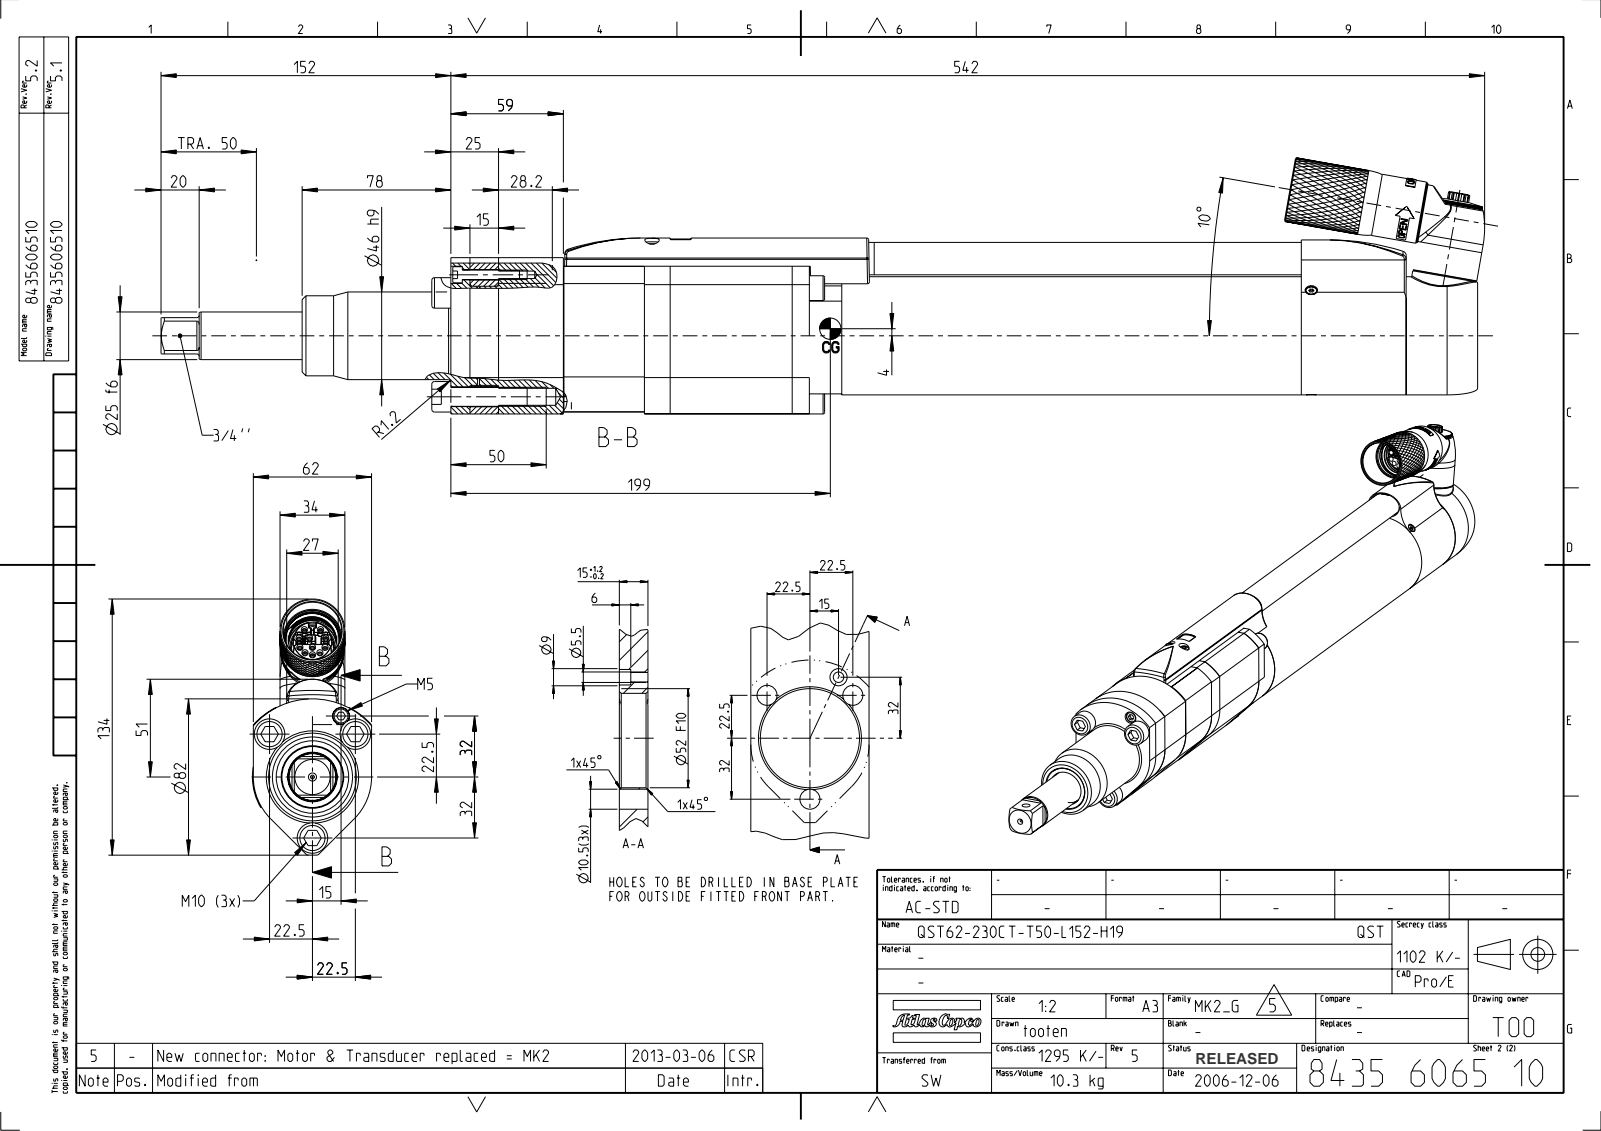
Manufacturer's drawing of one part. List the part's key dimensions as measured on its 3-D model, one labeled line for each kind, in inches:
Part name (STEP PRODUCT): QST62_REARCOVER_02; QST_CONNECTOR_02; QST62_230_CT_BODY; QST62_SPACER_01 (+3 more)
STEP written by: PRO/ENGINEER BY PARAMETRIC TECHNOLOGY CORPORATION, 2012420 (CONFIG_CONTROL_DESIGN)
Units: inches
Bodies: 10 solids, 2995 faces (1224 planar, 960 cylindrical, 811 other)
Overall size (bounding box): 27.33 × 5.291 × 2.444
Volume: 72.5 in³ · Surface area: 640.7 in²
Round holes (diameter × count): ⌀0.177 ×8, ⌀0.13 ×7, ⌀0.154 ×4, ⌀0.217 ×4, ⌀0.295 ×4, ⌀0.354 ×4, ⌀0.075 ×3, ⌀0.138 ×3, ⌀0.272 ×3, ⌀0.335 ×3, ⌀0.351 ×3, ⌀0.406 ×3
Round bosses / shafts (diameter × count): ⌀0.197 ×5, ⌀0.118 ×5, ⌀0.098 ×5, ⌀0.335 ×4, ⌀0.315 ×4, ⌀1.339 ×3, ⌀0.63 ×3, ⌀0.512 ×3
Partial cylindrical surfaces — rounded edges, fillets, slot ends (radius × count): R0.02 ×49, R0.008 ×8, R0.039 ×7, R0.079 ×5, R0.027 ×4, R0.047 ×4, R0.059 ×4, R0.207 ×4
Main face-to-face distances: 2.441, 0.591, 0.138, 1.339, 18.74, 9.862, 20.217, 20.807, 0.984, 0.394
Hole centre spacings: 0.886, 0.797, 0.582, 0.657, 0.909, 0.91, 1.139, 1.543
